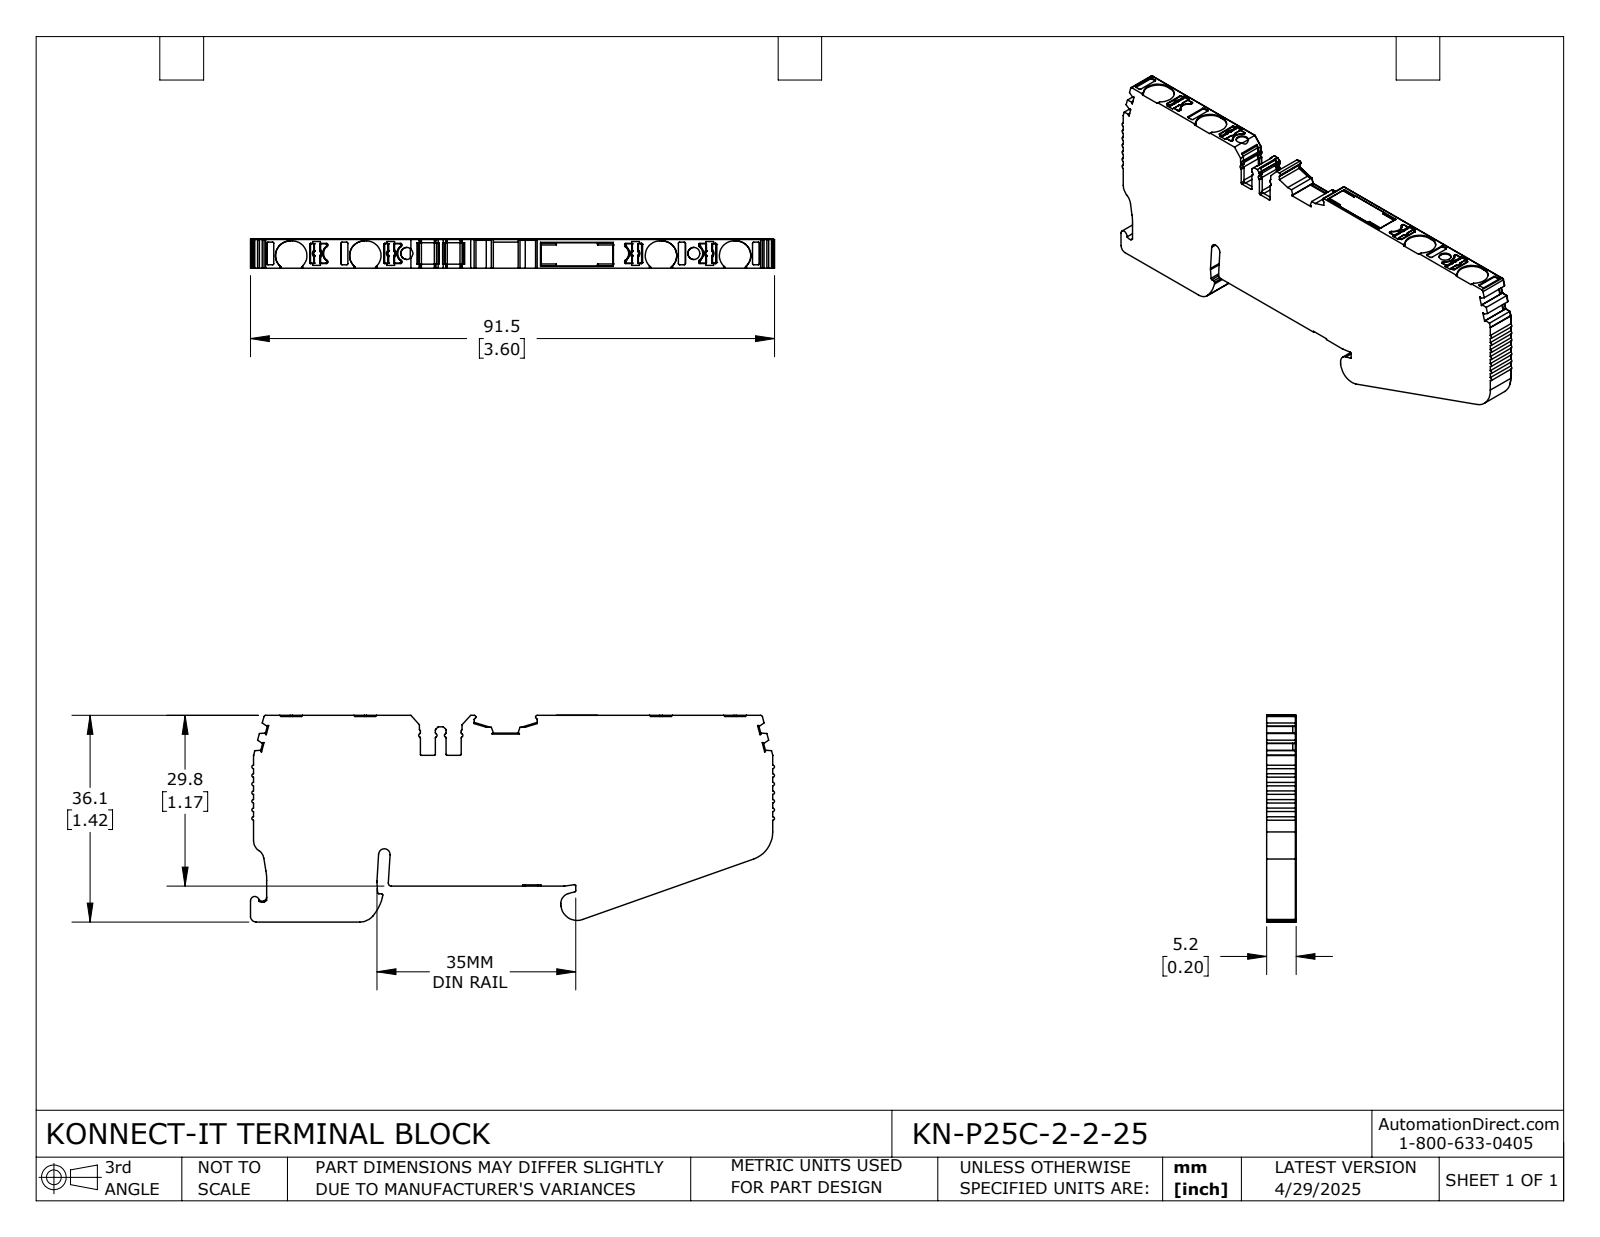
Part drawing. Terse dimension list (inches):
name: KN-P25C-2-2-25
written by: SolidWorks 2024 (CONFIG_CONTROL_DESIGN)
unit: in
bodies: 1 solid, 761 faces (399 planar, 291 cylindrical, 71 other)
size: 3.602 × 1.42 × 0.203
volume: 0.855 in³; area: 11.09 in²
holes: 2× ⌀0.083
rounds: 78× R0.008, 39× R0.012, 21× R0.004, 18× R0.02, 16× R0.006, 9× R0.016, 8× R0.1, 4× R0.059
face distances: 0.203, 1.166, 1.174, 0.246, 1.412, 1.42, 3.569, 0.197, 0.177, 0.047
hole spacings: 1.973
